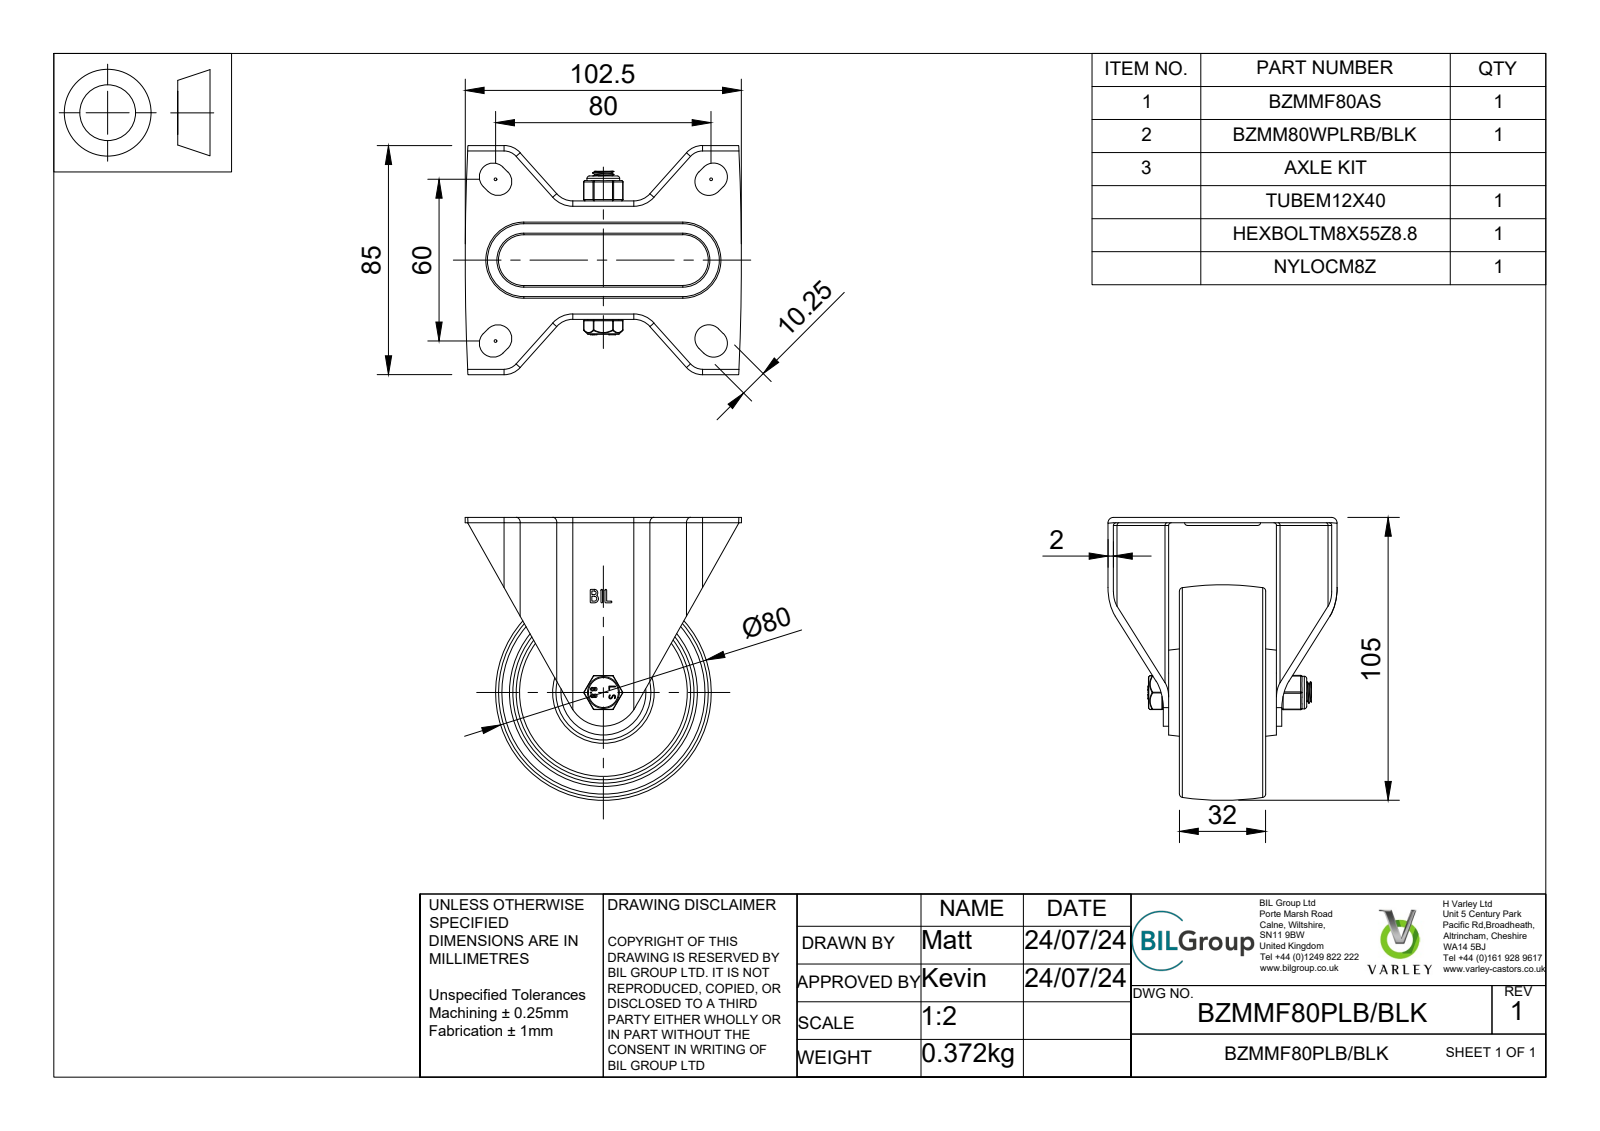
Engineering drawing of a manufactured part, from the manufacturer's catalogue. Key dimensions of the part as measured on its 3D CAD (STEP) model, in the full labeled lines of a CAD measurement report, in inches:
Part name (STEP PRODUCT): BZMMF80PLB/BLK v3; BZMMF80AS - 40 v2; ZINC PLATED, PRESSED STEEL BRACKET; BZMM80WPLRBBLK v1 (+7 more)
STEP written by: Autodesk Translation Framework v13.14.0.145 (AUTOMOTIVE_DESIGN)
Units: inches
Bodies: 15 solids, 449 faces (177 planar, 170 cylindrical, 102 other)
Overall size (bounding box): 4.134 × 4.035 × 3.346
Volume: 8.042 in³ · Surface area: 114.8 in²
Round holes (diameter × count): ⌀0.026 ×2, ⌀0.315 ×1, ⌀0.325 ×1, ⌀0.331 ×1, ⌀0.339 ×1, ⌀0.472 ×1, ⌀0.748 ×1, ⌀0.984 ×1
Round bosses / shafts (diameter × count): ⌀0.138 ×8, ⌀0.866 ×1, ⌀0.689 ×1, ⌀0.476 ×1, ⌀0.469 ×1, ⌀0.453 ×1, ⌀0.31 ×1, ⌀0.254 ×1
Partial cylindrical surfaces — rounded edges, fillets, slot ends (radius × count): R0.02 ×18, R0.01 ×12, R0.039 ×12, R0.079 ×8, R0.157 ×8, R0.202 ×8, R0.315 ×8, R0.013 ×4
Main face-to-face distances: 0.079, 0.748, 0.669, 0.906, 0.203, 0.984, 1.654, 0.236, 1.575, 0.124
Hole centre spacings: 0.127, 0.098
